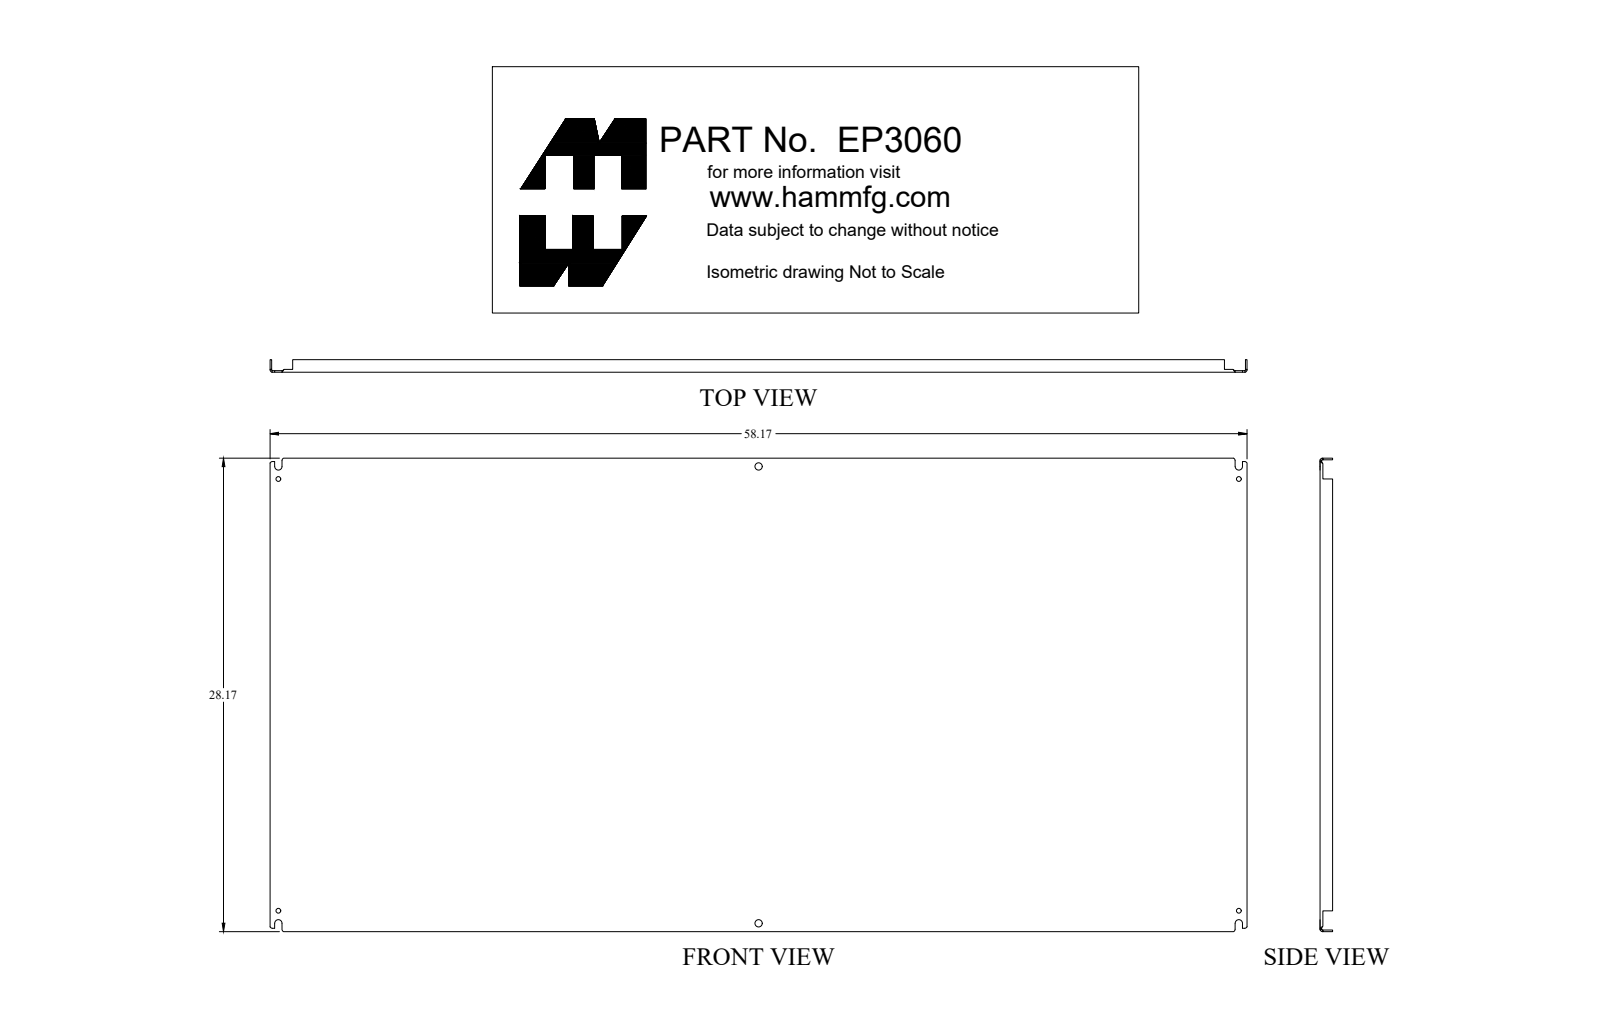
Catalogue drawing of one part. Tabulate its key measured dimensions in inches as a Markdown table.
| quantity | value |
| --- | --- |
| part name | EP3060 |
| STEP written by | SolidWorks 2018 (AUTOMOTIVE_DESIGN) |
| units | inches |
| bodies | 1 solid, 132 faces (74 planar, 42 cylindrical, 16 other) |
| overall size | 58.17 × 28.17 × 0.75 |
| volume | 165 in³ |
| surface area | 3 491 in² |
| round holes (diameter × count) | 0.281 × 4, 0.437 × 2 |
| partial cylindrical surfaces (radius × count) | 0.048 × 4, 0.063 × 4, 0.143 × 4, 0.219 × 4 |
| main face-to-face distances | 0.095, 28.075, 28.17, 27.98, 58.075, 58.17, 57.98, 0.75, 0.655, 0.171 |
| hole center spacings | 28.604, 38.944, 25.688, 57.188, 62.693, 27.188 |
